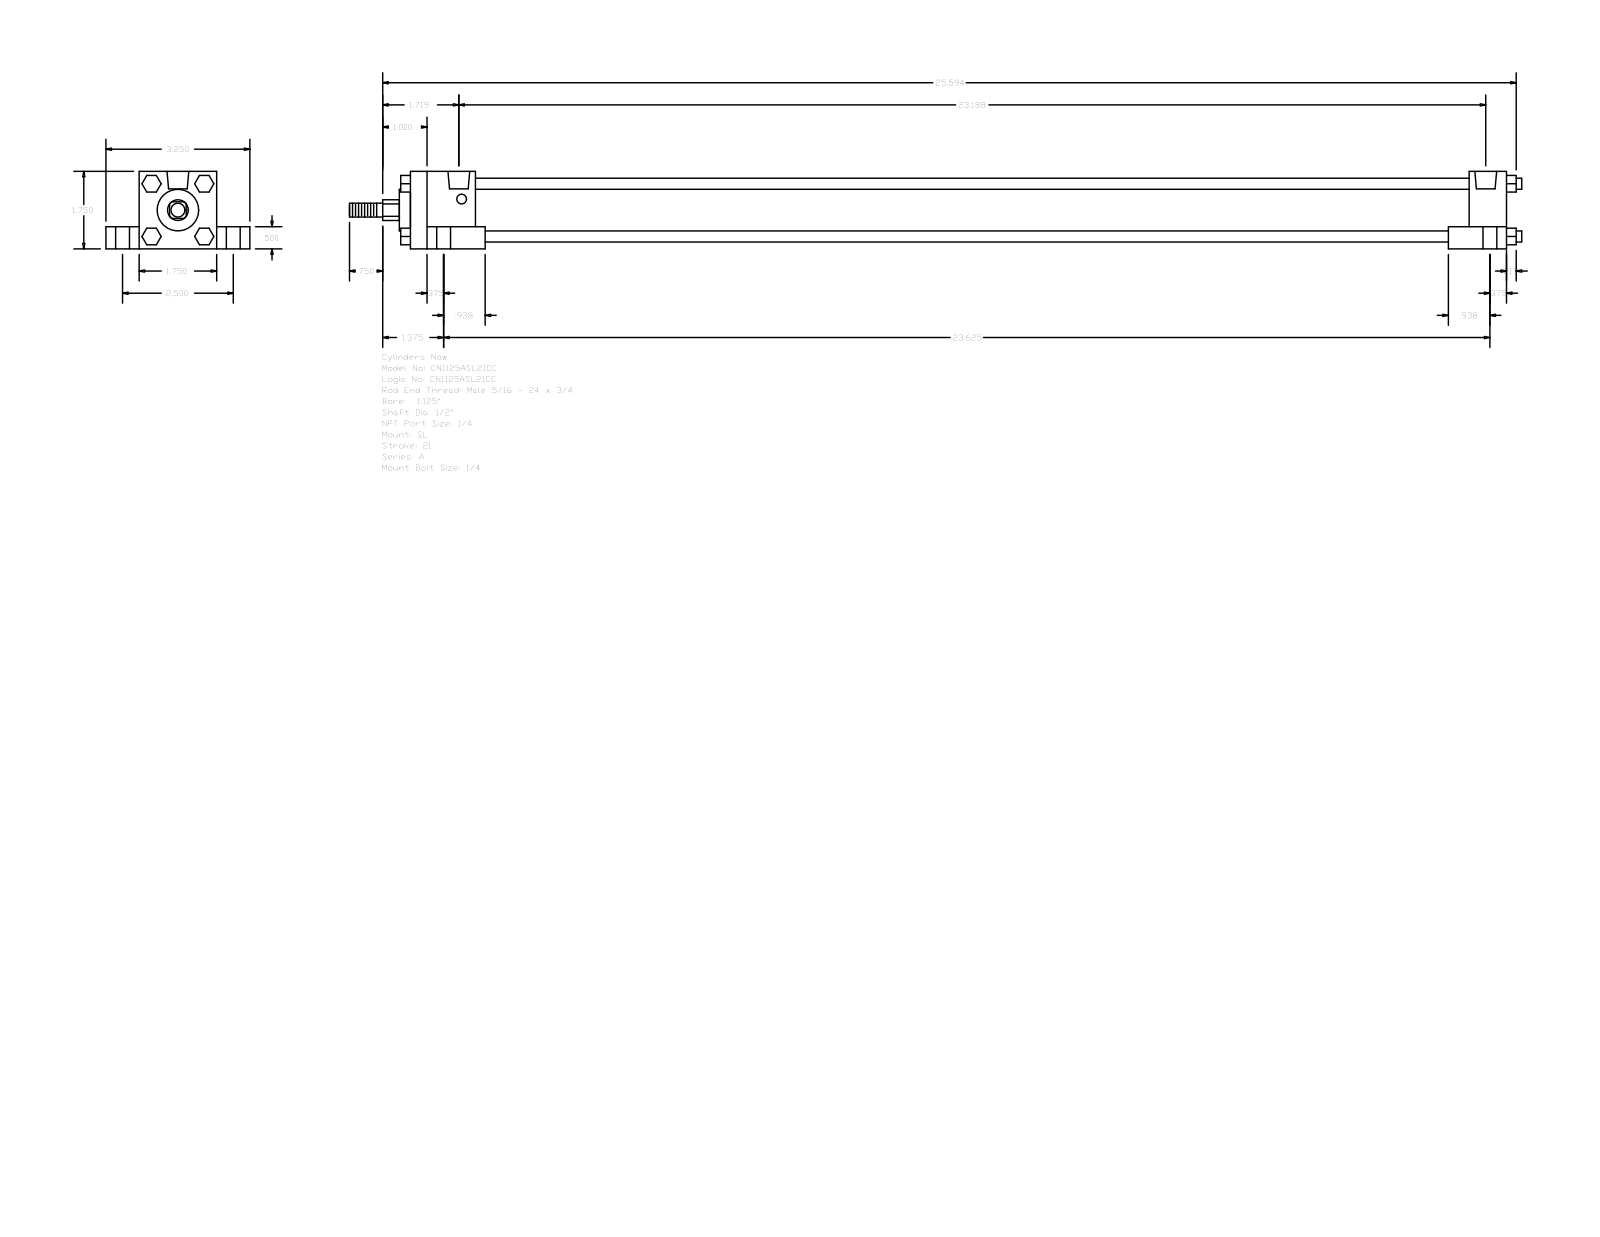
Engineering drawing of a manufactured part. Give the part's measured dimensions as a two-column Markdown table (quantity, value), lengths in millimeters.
| quantity | value |
| --- | --- |
| part name | A_SL__0112_0.5 |
| STEP written by | GSSL Pune (CONFIG_CONTROL_DESIGN) |
| units | millimeters |
| bodies | 0 solids, 150 faces (114 planar, 36 cylindrical, 0 other) |
| overall size | 672.31 × 82.55 × 44.45 |
| round holes (diameter × count) | 5.56 × 4, 7.94 × 4, 14.29 × 4, 12.49 × 2 |
| round bosses / shafts (diameter × count) | 6.35 × 4, 31.88 × 1, 23.81 × 1, 12.7 × 1, 7.94 × 1 |
| partial cylindrical surfaces (radius × count) | 5.94 × 1 |
| main face-to-face distances | 44.46, 31.76, 12.7, 19.04, 63.5, 591.34, 628.64, 607.21, 21.43, 37.3 |
| hole center spacings | 31.84, 32, 32.93, 33.39, 63.5, 585.79, 590.61, 592.19 |
